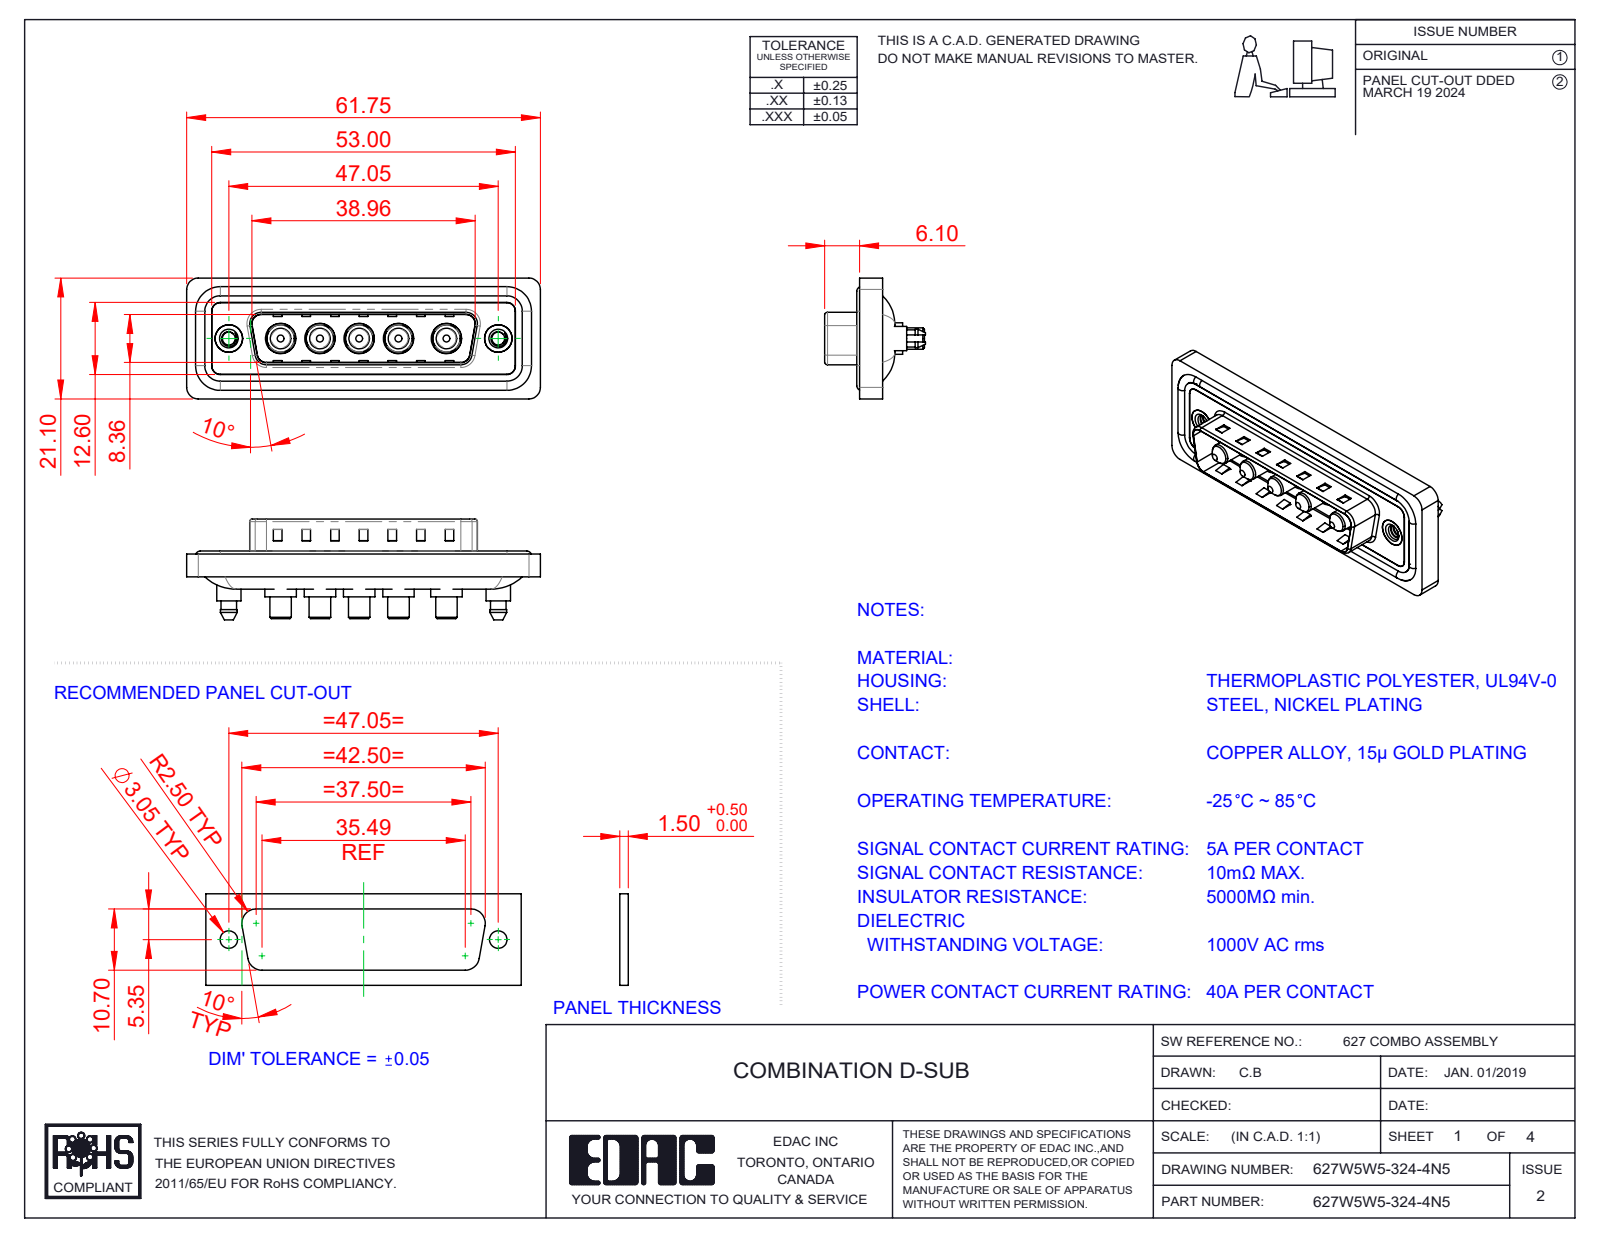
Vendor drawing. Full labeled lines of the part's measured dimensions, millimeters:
Part name (STEP PRODUCT): 627W5W5-324-4N5; 627Combo Housing_5W5; 627Combo Shell Rear_25 Contacts; 627Combo Waterproof Housing_25 Contacts (+3 more)
STEP written by: SolidWorks 2023 (CONFIG_CONTROL_DESIGN)
Units: millimetres
Bodies: 17 solids, 728 faces (275 planar, 315 cylindrical, 138 other)
Overall size (bounding box): 61.75 × 21.1 × 17.6
Volume: 7 699 mm³ · Surface area: 12 184 mm²
Round holes (diameter × count): ⌀4.85 ×5, ⌀5.3 ×5, ⌀2.26 ×2, ⌀4 ×2, ⌀4.8 ×2, ⌀5 ×2
Round bosses / shafts (diameter × count): ⌀5.5 ×5, ⌀5.2 ×5, ⌀4.75 ×5, ⌀3.75 ×5, ⌀3.6 ×5, ⌀1.6 ×4, ⌀5.4 ×2, ⌀4.9 ×2
Partial cylindrical surfaces — rounded edges, fillets, slot ends (radius × count): R1.5 ×24, R2 ×18, R1.6 ×10, R0.5 ×8, R2.1 ×5, R0.25 ×4, R0.6 ×4, R0.65 ×4
Main face-to-face distances: 0.4, 1.5, 3.1, 1.1, 0.5, 1.6, 2.9, 0.82, 9.58, 5.65
Hole centre spacings: 6.86, 9.04, 13.73, 38.01, 6.87, 8.37, 8.38, 9.05
